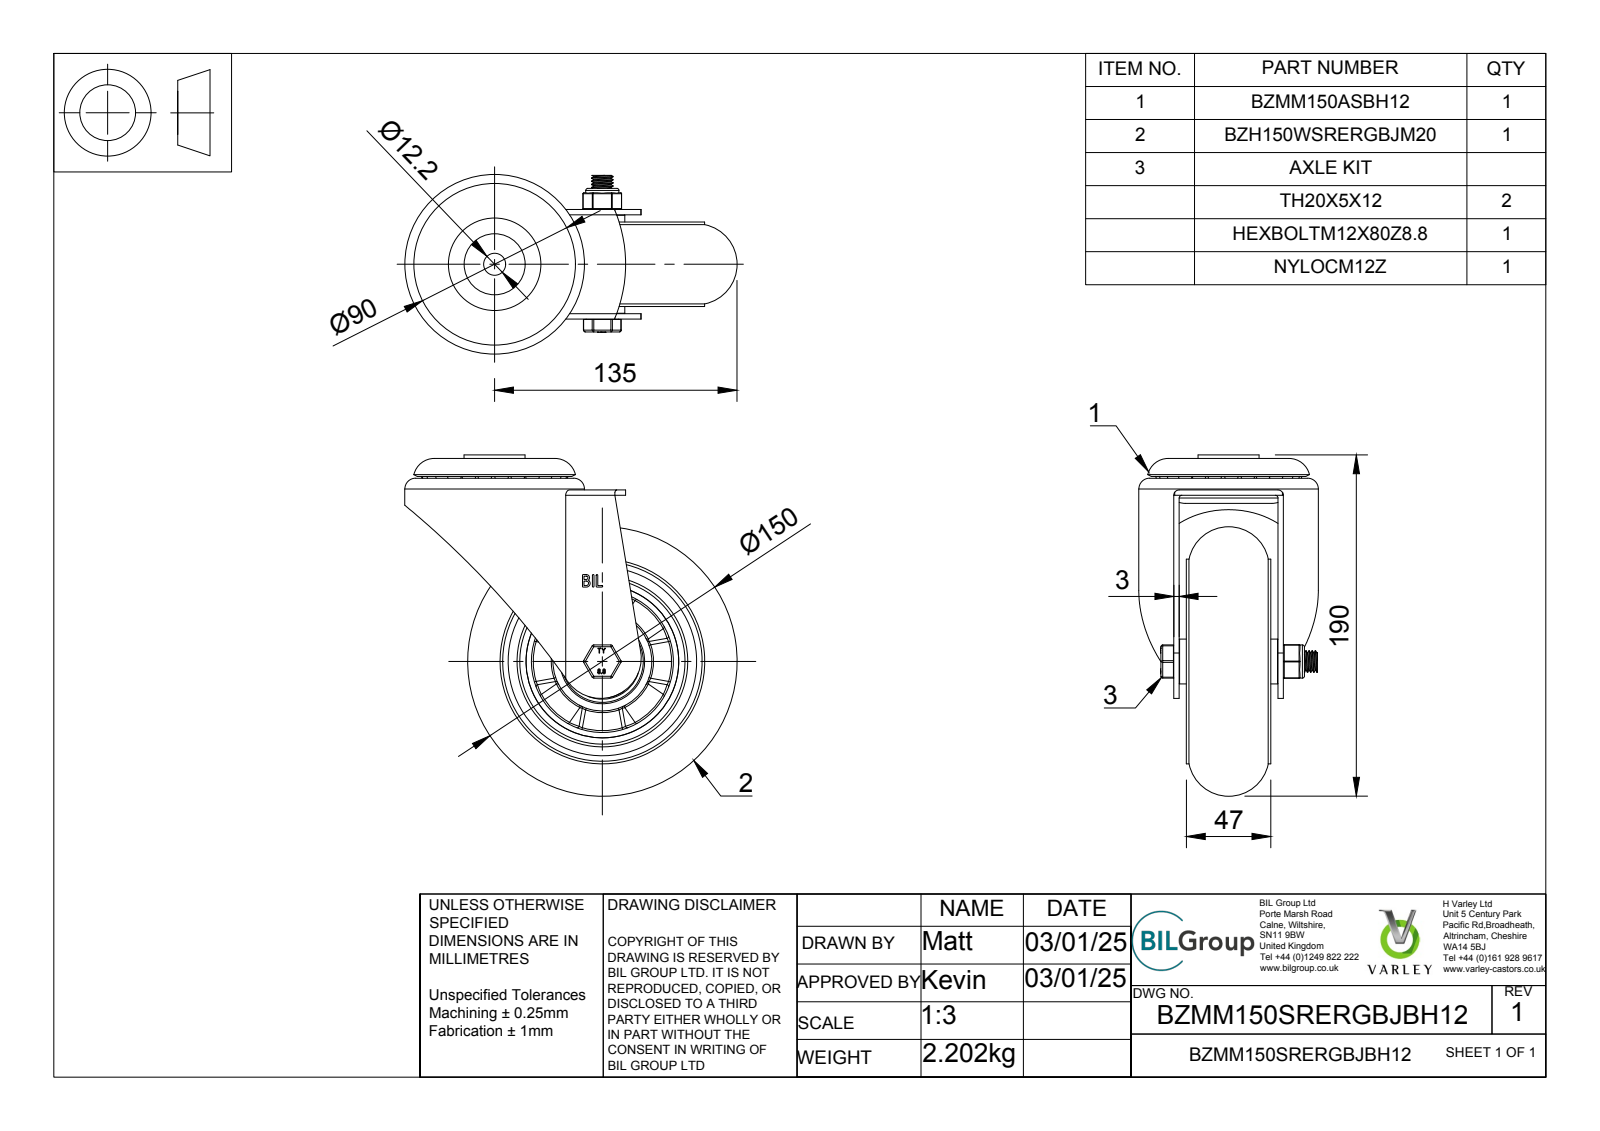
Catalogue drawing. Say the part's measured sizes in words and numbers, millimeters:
The part is named "BZMM150SRERGBJBH12 v3; BZMM150ASBH12 - 55 v1; ZINC PLATED, PRESSED STEEL FORKS; ZINC PLATED, PRESSED STEEL HEAD (+6 more)". Its 3-D file was written by "Autodesk Translation Framework v13.20.0.188 (AP242_MANAGED_MODEL_BASED_3D_ENGINEERING_MIM_LF)". It is 81 solids with 1237 faces: 418 planar, 199 cylindrical and 620 other. Overall it measures 190 by 185 by 100 millimeters. Its volume is 710 442 cubic millimeters and its surface area 232 829 square millimeters. Round holes: 1 of diameter 12, 1 of diameter 12.2, 1 of diameter 12.5, 1 of diameter 14, 1 of diameter 20, 1 of diameter 28.5, 1 of diameter 30.8, 1 of diameter 39, 1 of diameter 40.3, 1 of diameter 40.5, 1 of diameter 42, 1 of diameter 43. Round bosses or shafts: 1 of diameter 114, 1 of diameter 100, 1 of diameter 95, 1 of diameter 63, 1 of diameter 55, 1 of diameter 40.8, 1 of diameter 34, 1 of diameter 31.3. Partial cylindrical surfaces (rounded edges, fillets, slot ends): 18 of radius 0.5, 12 of radius 1, 4 of radius 1.5, 2 of radius 3, 1 of radius 16.5, 1 of radius 19.5, 1 of radius 22.56, 1 of radius 78. The main face-to-face distances are 3, 58, 8, 11, 5, 14, 6, 31, 2.5, 50.
